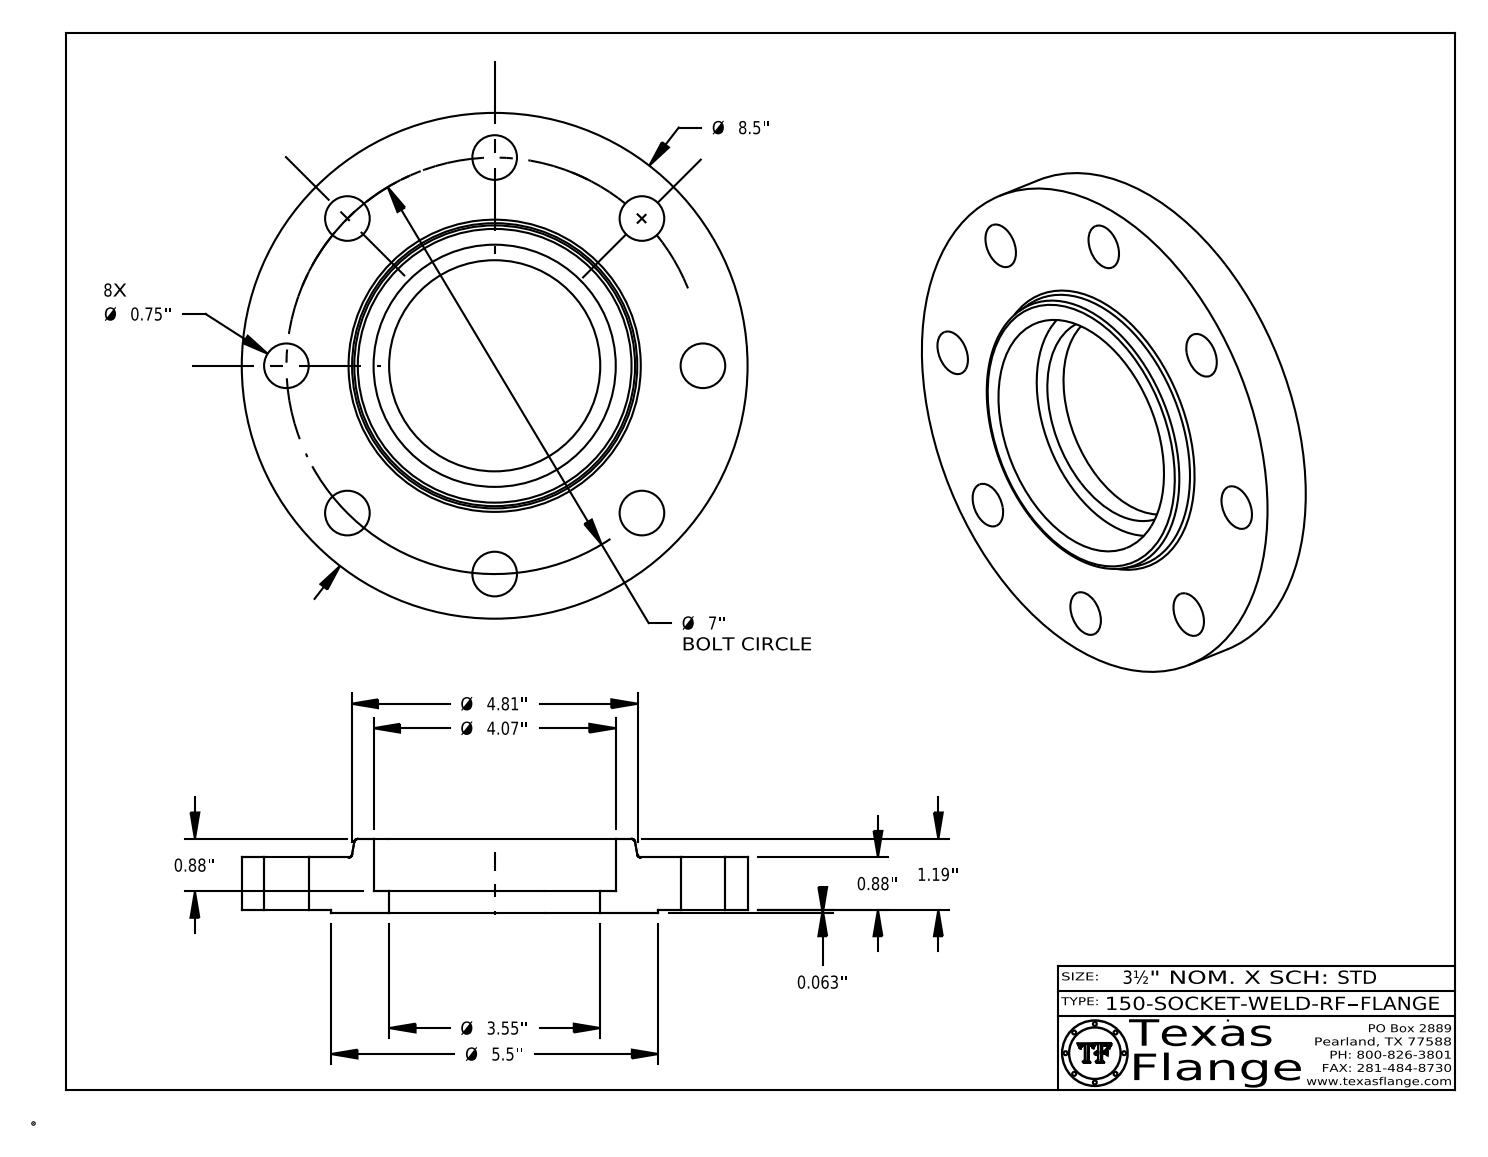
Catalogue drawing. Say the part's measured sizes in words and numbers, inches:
The part is named "150-SOCKET-WELD-RF". Its 3-D file was written by "CATIA V5 STEP AP214 (AUTOMOTIVE_DESIGN)". It is 1 solid with 420 faces: 370 planar, 44 cylindrical and 6 other. Overall it measures 8.5 by 8.5 by 1.253 inches. Its volume is 38.68 cubic inches and its surface area 146.7 square inches. Round holes: 8 of diameter 0.75, 1 of diameter 0.495, 1 of diameter 3.548, 1 of diameter 4.07. Round bosses or shafts: 8 of diameter 0.03, 1 of diameter 8.5, 1 of diameter 5.5, 1 of diameter 0.39. The main face-to-face distances are 0.88, 0.063, 0.943, 1.253, 1.19, 0.31, 0.372, 0.31, 0.57, 0.88. The hole center spacings are 3.5, 2.679, 4.95, 6.467, 1.366, 3.889, 5.82, 6.865.
